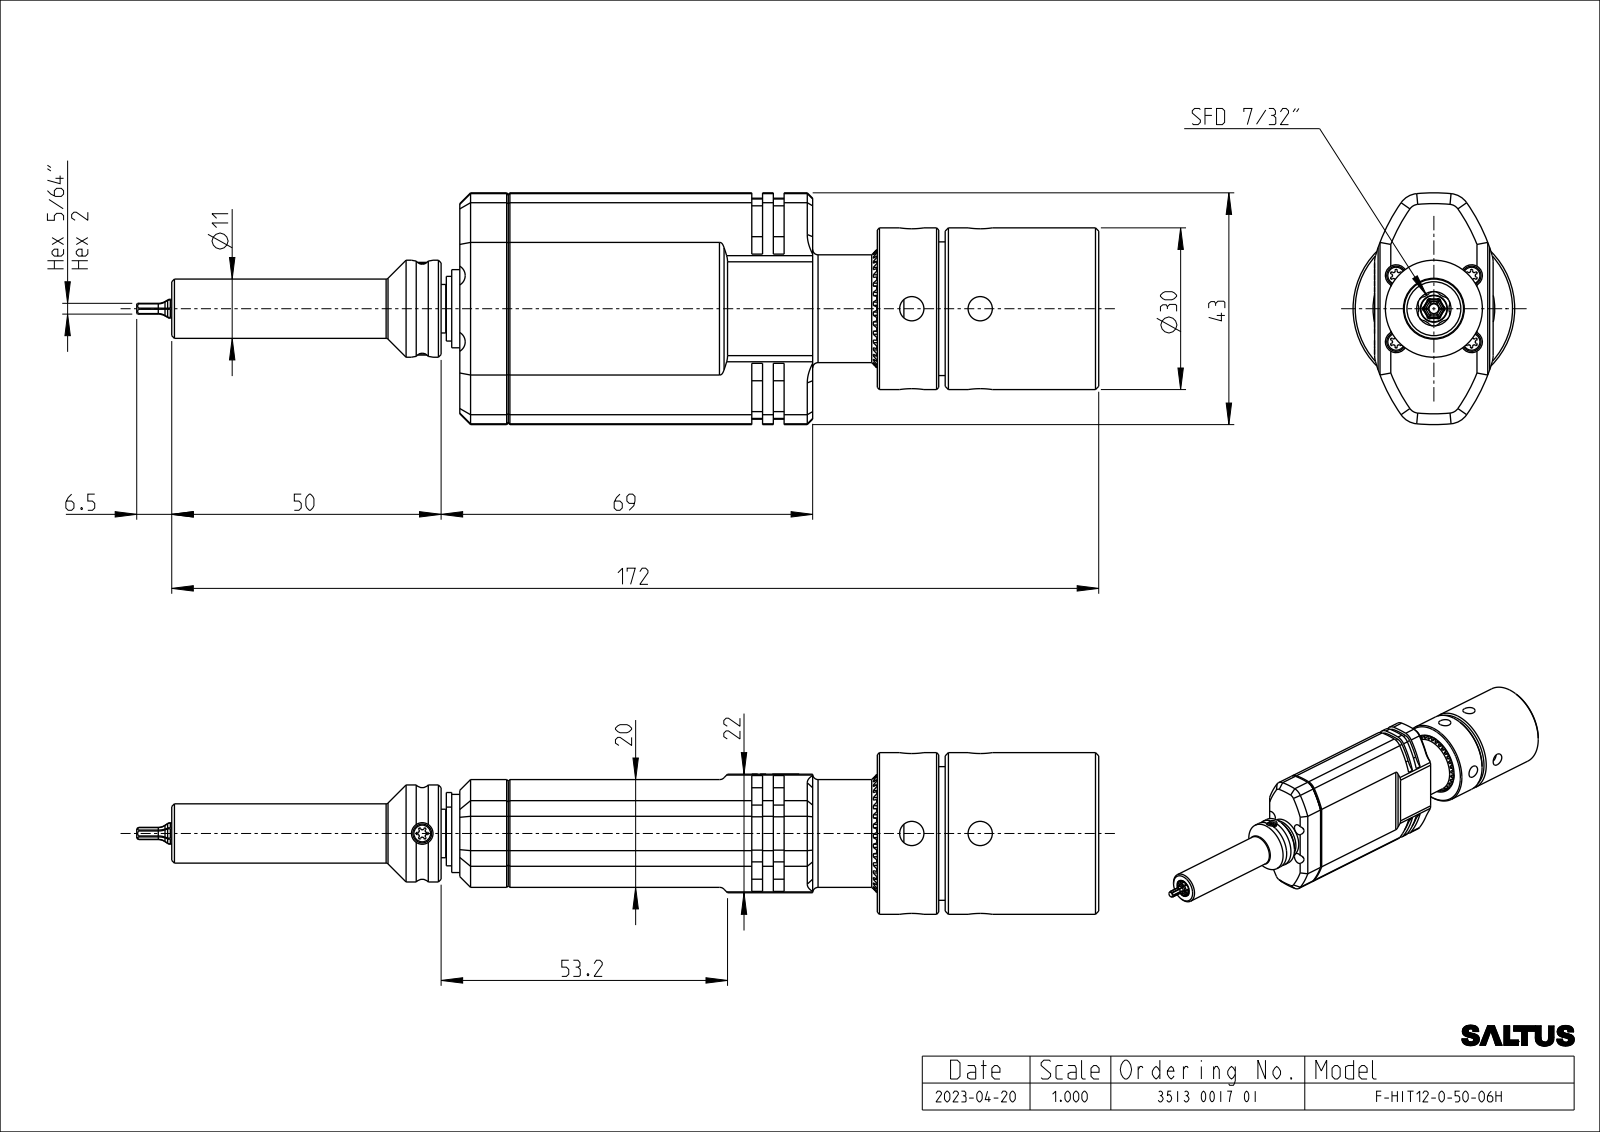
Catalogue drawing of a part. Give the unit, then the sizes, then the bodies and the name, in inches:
Units: inches
Overall size (bounding box): 7.03 × 1.693 × 1.181
Round holes (diameter × count): ⌀0.157 ×5, ⌀0.177 ×4, ⌀0.047 ×2, ⌀0.339 ×1, ⌀0.358 ×1, ⌀0.866 ×1, ⌀0.992 ×1, ⌀1.043 ×1
Round bosses / shafts (diameter × count): ⌀0.138 ×5, ⌀1.181 ×1, ⌀1.024 ×1, ⌀0.976 ×1, ⌀0.933 ×1, ⌀0.795 ×1, ⌀0.787 ×1, ⌀0.709 ×1
Partial cylindrical surfaces — rounded edges, fillets, slot ends (radius × count): R0.008 ×42, R0.012 ×30, R0.039 ×18, R0.098 ×12, R0.157 ×8, R1.299 ×6, R1.339 ×6, R0.118 ×4
Main face-to-face distances: 0.787, 0.039, 0.827, 2.091, 4.669, 2.579, 0.866, 1.618, 0.472, 3.051
Hole centre spacings: 0.367, 0.176, 0.245, 0.317, 0.484, 0.5, 0.537, 0.551
Volume: 5.415 in³ · Surface area: 29.67 in²
Bodies: 1 solid, 1277 faces (658 planar, 411 cylindrical, 208 other)
Part name (STEP PRODUCT): 3513001701_SW0001
STEP written by: CREO PARAMETRIC BY PTC INC, 2020281 (CONFIG_CONTROL_DESIGN)
